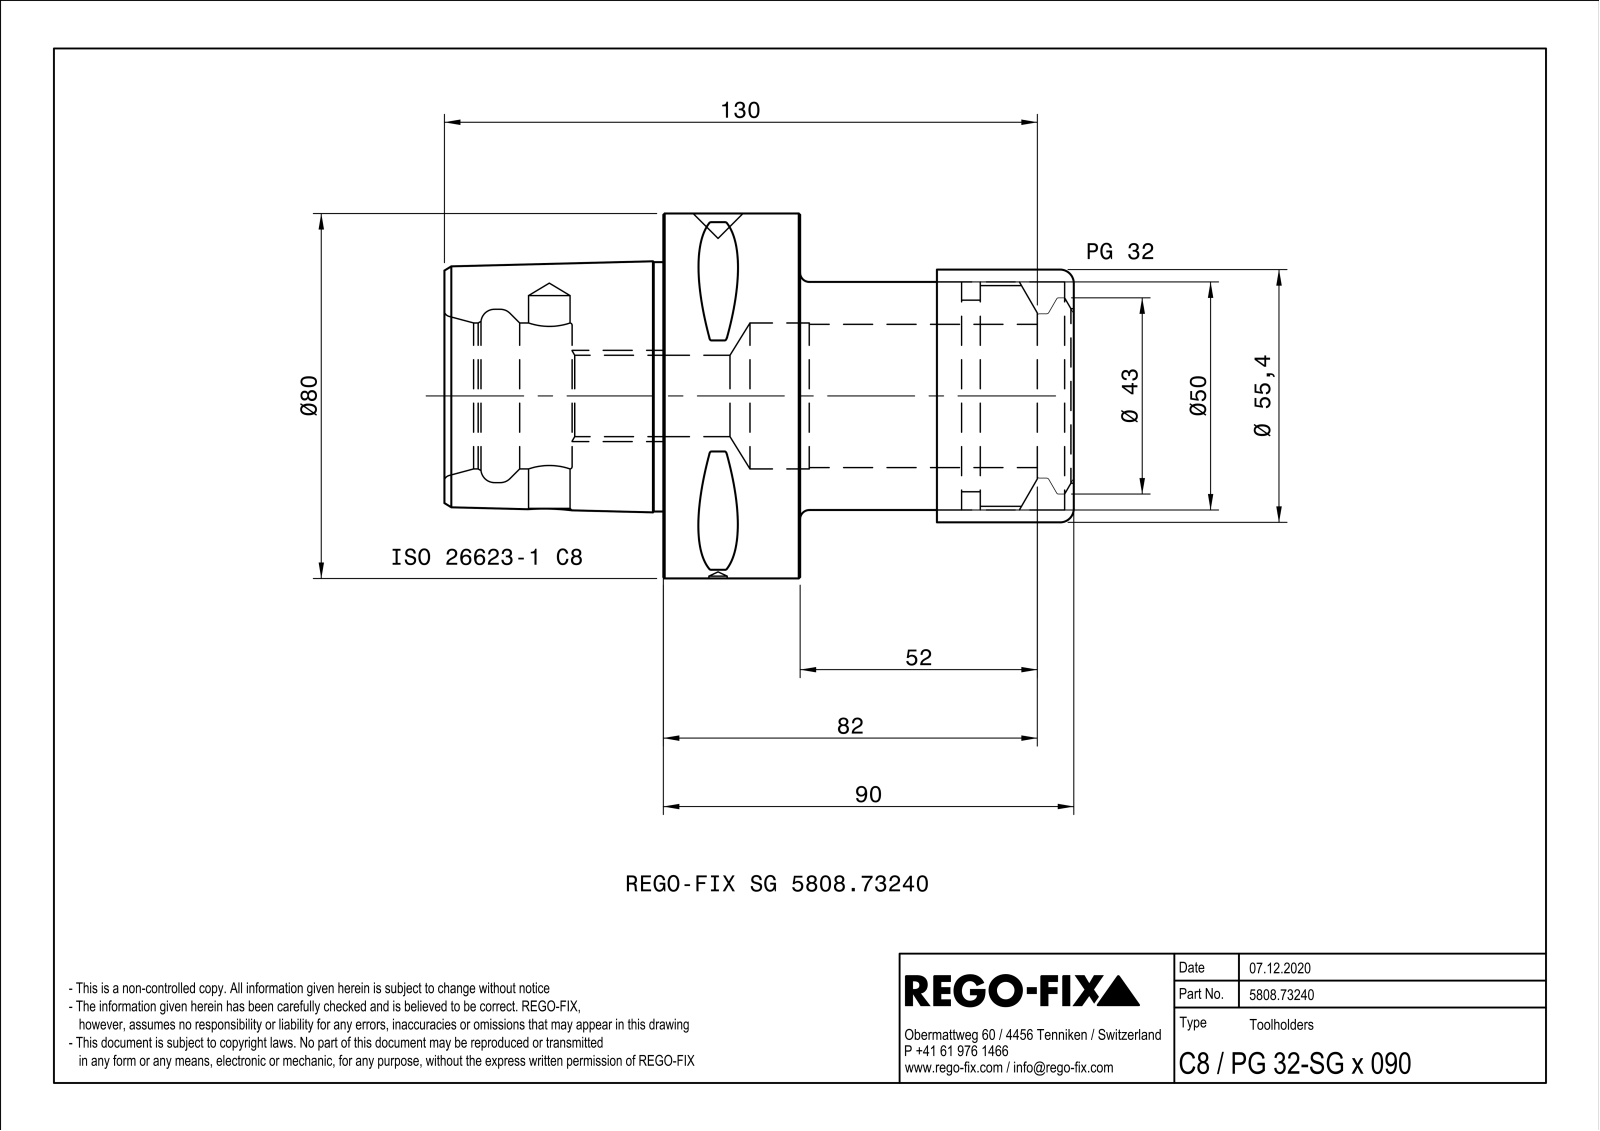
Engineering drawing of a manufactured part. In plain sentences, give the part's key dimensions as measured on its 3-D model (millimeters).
The part is named "NOCUT". Its 3-D file was written by "SIEMENS PLM Software Solid Edge ST10 (AUTOMOTIVE_DESIGN)". It is 3 solids with 149 faces: 30 planar, 35 cylindrical and 84 other. Overall it measures 138 by 80 by 80 millimeters. Its volume is 322 884 cubic millimeters and its surface area 69 180 square millimeters. Round holes: 1 of diameter 4, 1 of diameter 6, 1 of diameter 9.1, 1 of diameter 15.5, 1 of diameter 17.84, 1 of diameter 26.92, 1 of diameter 28.5, 1 of diameter 32, 1 of diameter 33, 1 of diameter 38, 1 of diameter 38.25, 1 of diameter 48.38. Round bosses or shafts: 1 of diameter 80, 1 of diameter 55.4, 1 of diameter 55, 1 of diameter 50, 1 of diameter 43, 1 of diameter 42, 1 of diameter 36, 1 of diameter 31.6. Partial cylindrical surfaces (rounded edges, fillets, slot ends): 8 of radius 0.5. The main face-to-face distances are 30, 60, 90, 138, 78, 48, 28, 108, 50, 80. The hole center spacings are 37.
